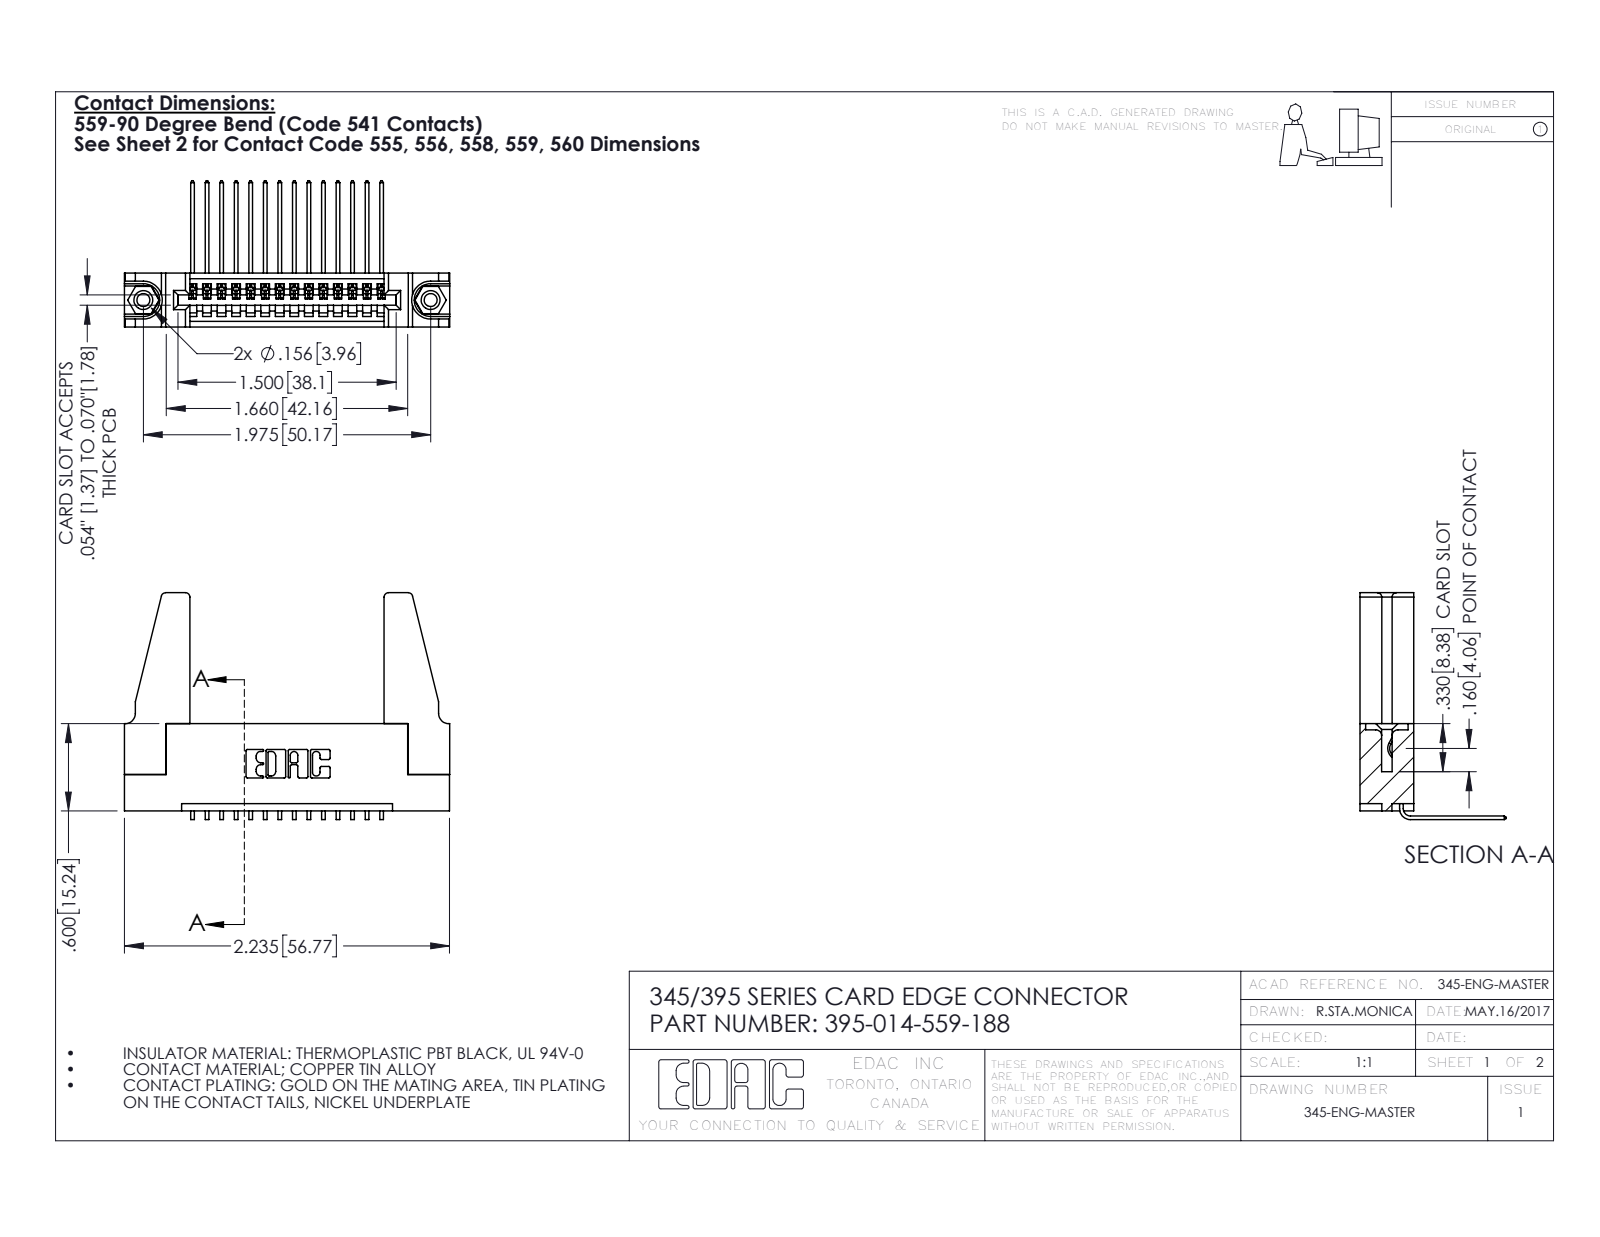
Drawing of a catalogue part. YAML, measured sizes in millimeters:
part_name: "395-014-559-188; 345-250-001_345-250-001-102; 345-292-001_558 559 Tail - 1; 345 Part_Flush Mounting Lugs - 0.156 Dia-TH (+1 more)"
step_written_by: "SolidWorks 2016 (CONFIG_CONTROL_DESIGN)"
units: millimeters
bodies: {solids: 19, faces: 1090, planar: 740, cylindrical: 334, other: 16}
overall_size: [56.8, 39.6, 25.5]
volume: 8470
surface_area: 9948
round_holes:
  - {diameter: 2.3, count: 2}
  - {diameter: 3.2, count: 2}
  - {diameter: 4, count: 2}
  - {diameter: 1.6, count: 1}
round_bosses_or_shafts:
  - {diameter: 3.9, count: 2}
partial_cylinders:
  - {radius: 0.2, count: 28}
  - {radius: 0.3, count: 22}
  - {radius: 0.8, count: 8}
  - {radius: 0.2, count: 6}
  - {radius: 0.8, count: 6}
  - {radius: 0.7, count: 3}
  - {radius: 0.8, count: 2}
  - {radius: 1, count: 2}
face_to_face_distances: [9.4, 1.8, 7.6, 5.1, 2.5, 6.9, 0.6, 5.7, 3.8, 3.8]
hole_center_spacings: [6.9, 44.2, 50.2]
